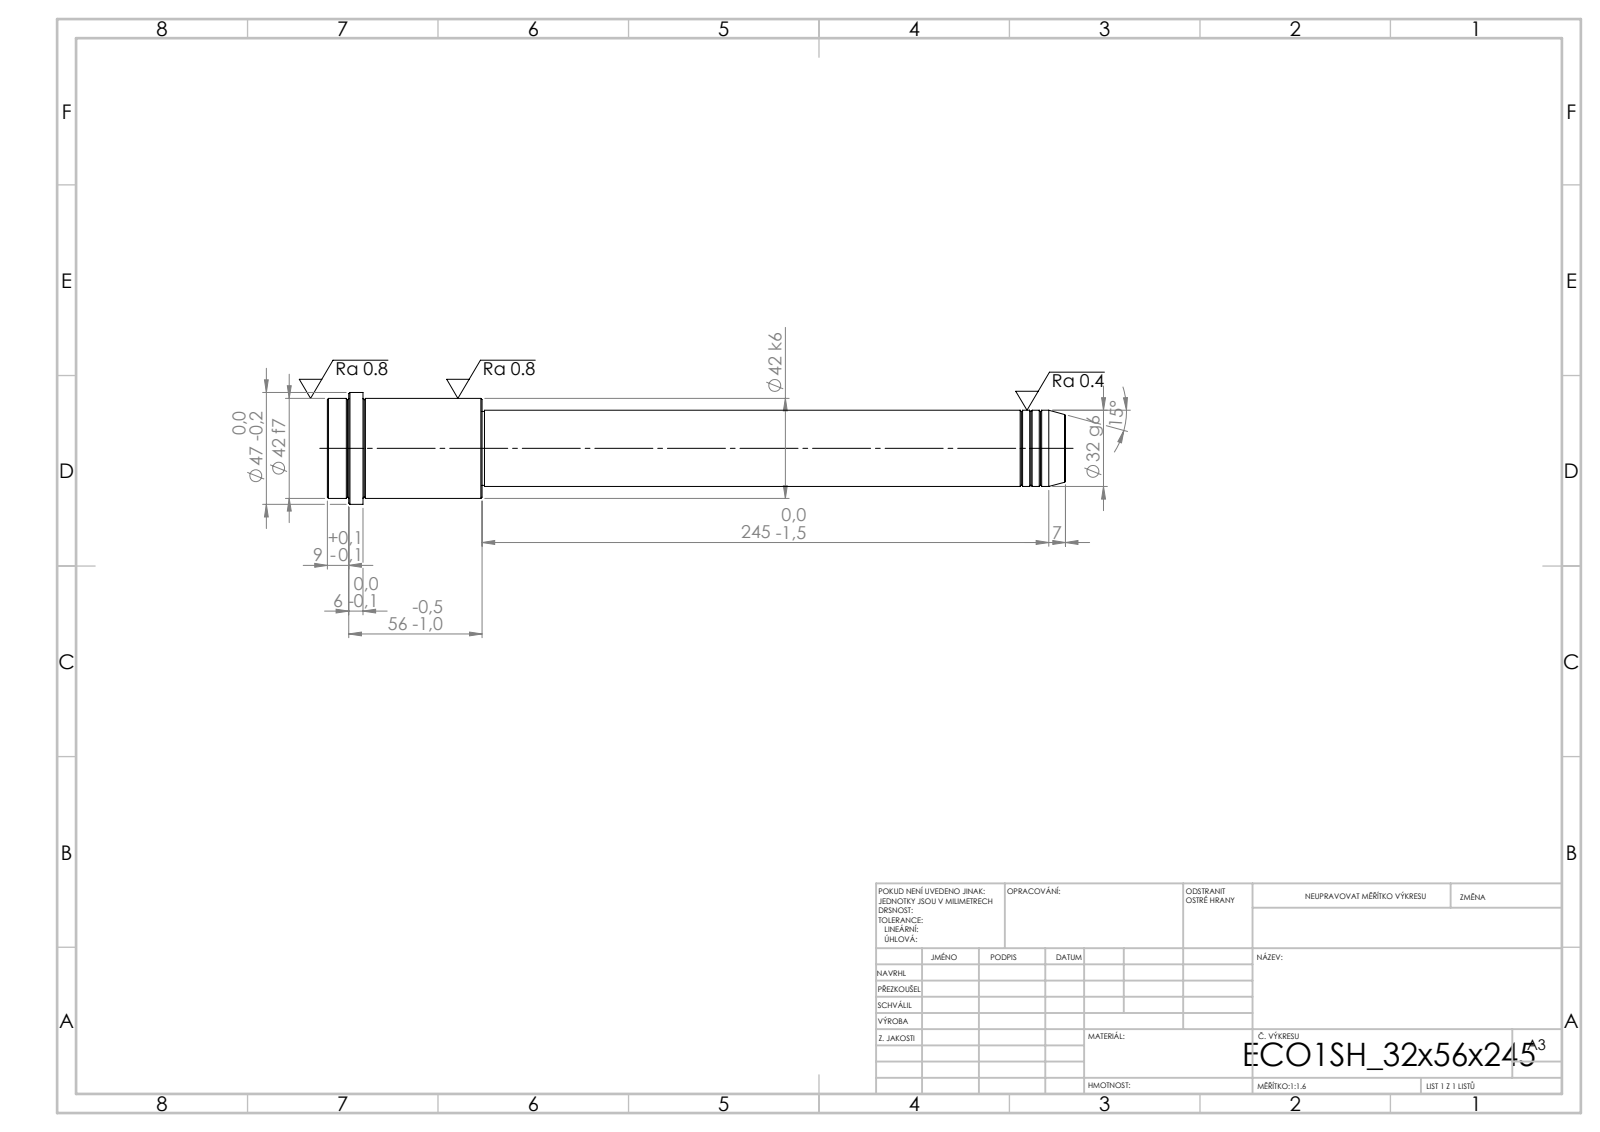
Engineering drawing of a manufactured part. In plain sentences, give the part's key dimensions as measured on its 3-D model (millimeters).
Its 3-D file was written by "SolidWorks 2019 (CONFIG_CONTROL_DESIGN)". It is 1 solid with 52 faces: 6 planar, 16 cylindrical and 30 other. Overall it measures 310 by 47 by 47 millimeters. Its volume is 288 235 cubic millimeters and its surface area 36 847 square millimeters. Round bosses or shafts: 1 of diameter 47, 1 of diameter 42, 1 of diameter 32, 1 of diameter 31. The main face-to-face distances are 310, 245, 65, 295, 50, 15, 301, 56, 6, 9.
